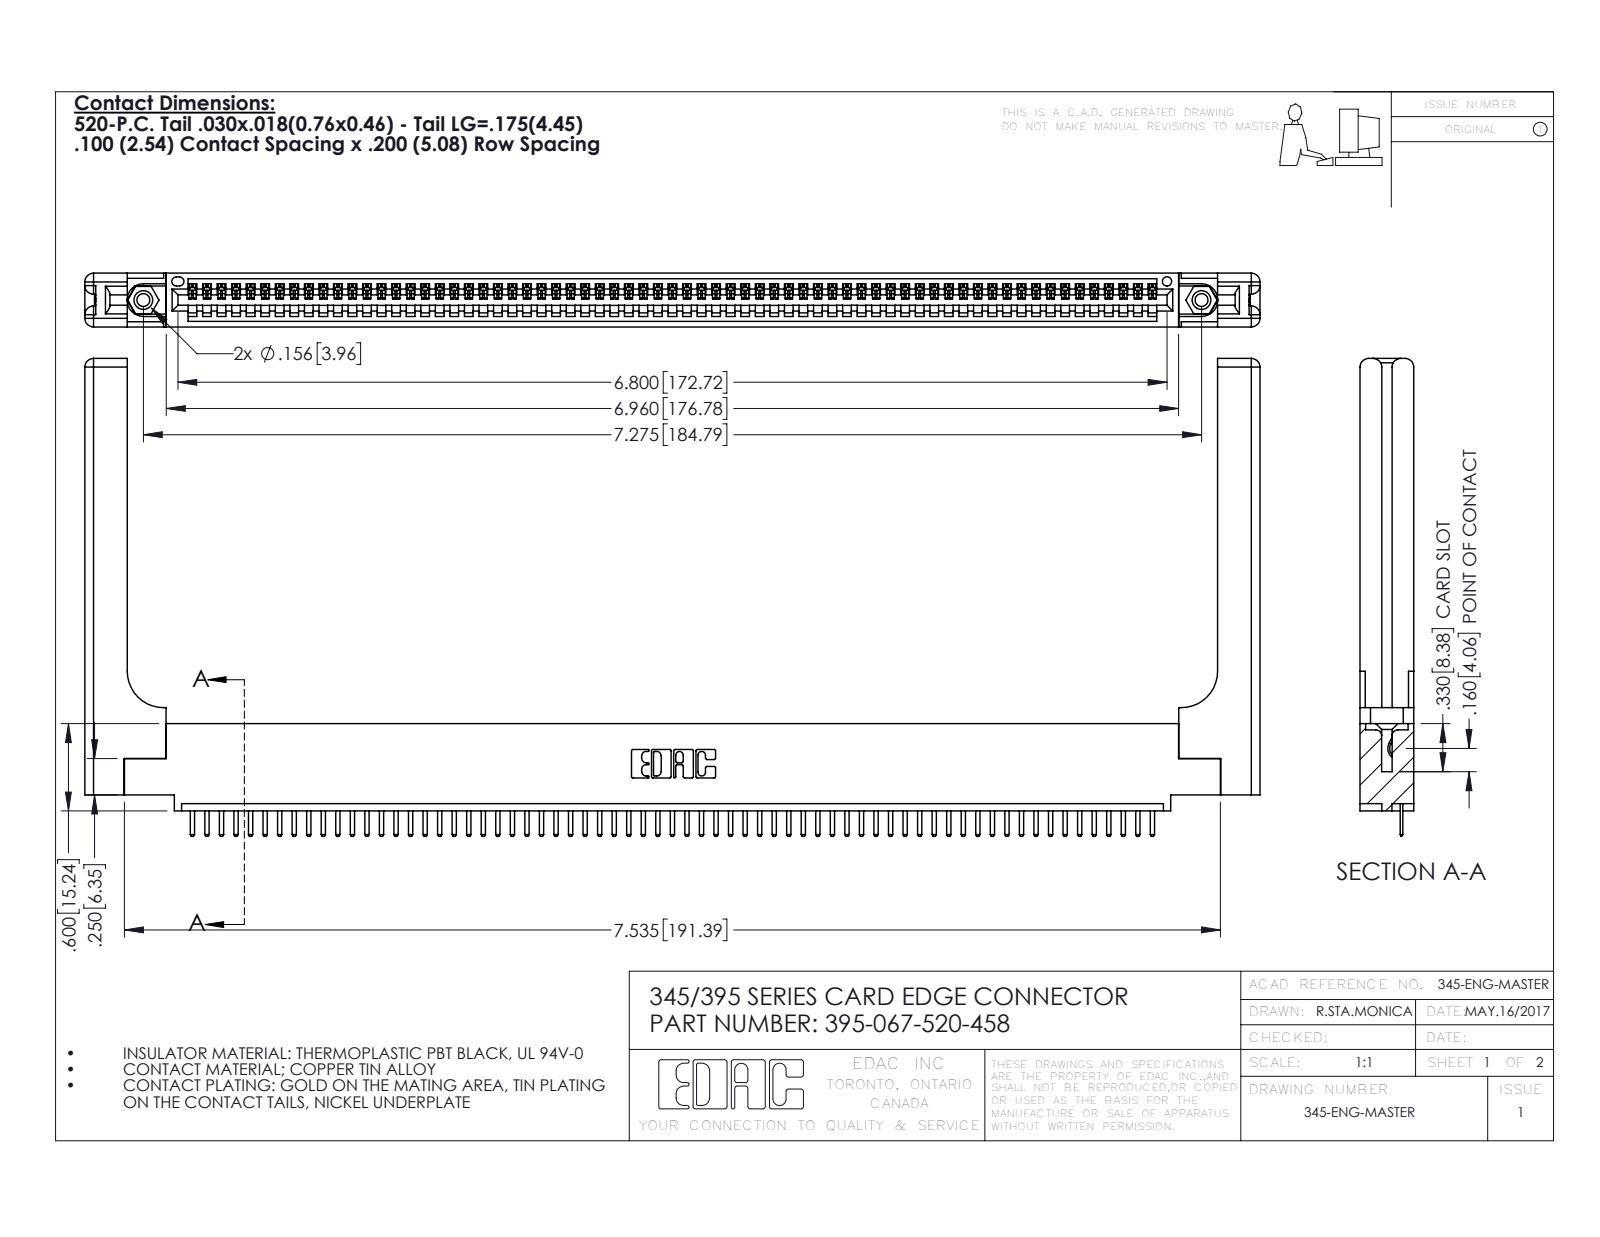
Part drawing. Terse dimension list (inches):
name: 345-292-001_345-293-120; 345 Part_0.110 Offset - 0.156 Dia-TH; 345-220-058_345-220-058; 395-067-520-458 (+1 more)
written by: SolidWorks 2016 (CONFIG_CONTROL_DESIGN)
unit: in
bodies: 72 solids, 4540 faces (3046 planar, 1434 cylindrical, 60 other)
size: 8.079 × 3.285 × 0.37
volume: 1.705 in³; area: 47.92 in²
holes: 2× ⌀0.089, 2× ⌀0.125, 2× ⌀0.156, 1× ⌀0.064
bosses: 2× ⌀0.155
rounds: 136× R0.01, 134× R0.006, 22× R0.01, 16× R0.06, 6× R0.007, 6× R0.031, 3× R0.026, 2× R0.03
face distances: 0.072, 0.37, 0.298, 0.098, 0.272, 0.025, 0.2, 0.225, 0.148, 0.15
hole spacings: 0.27, 7.039, 7.275
